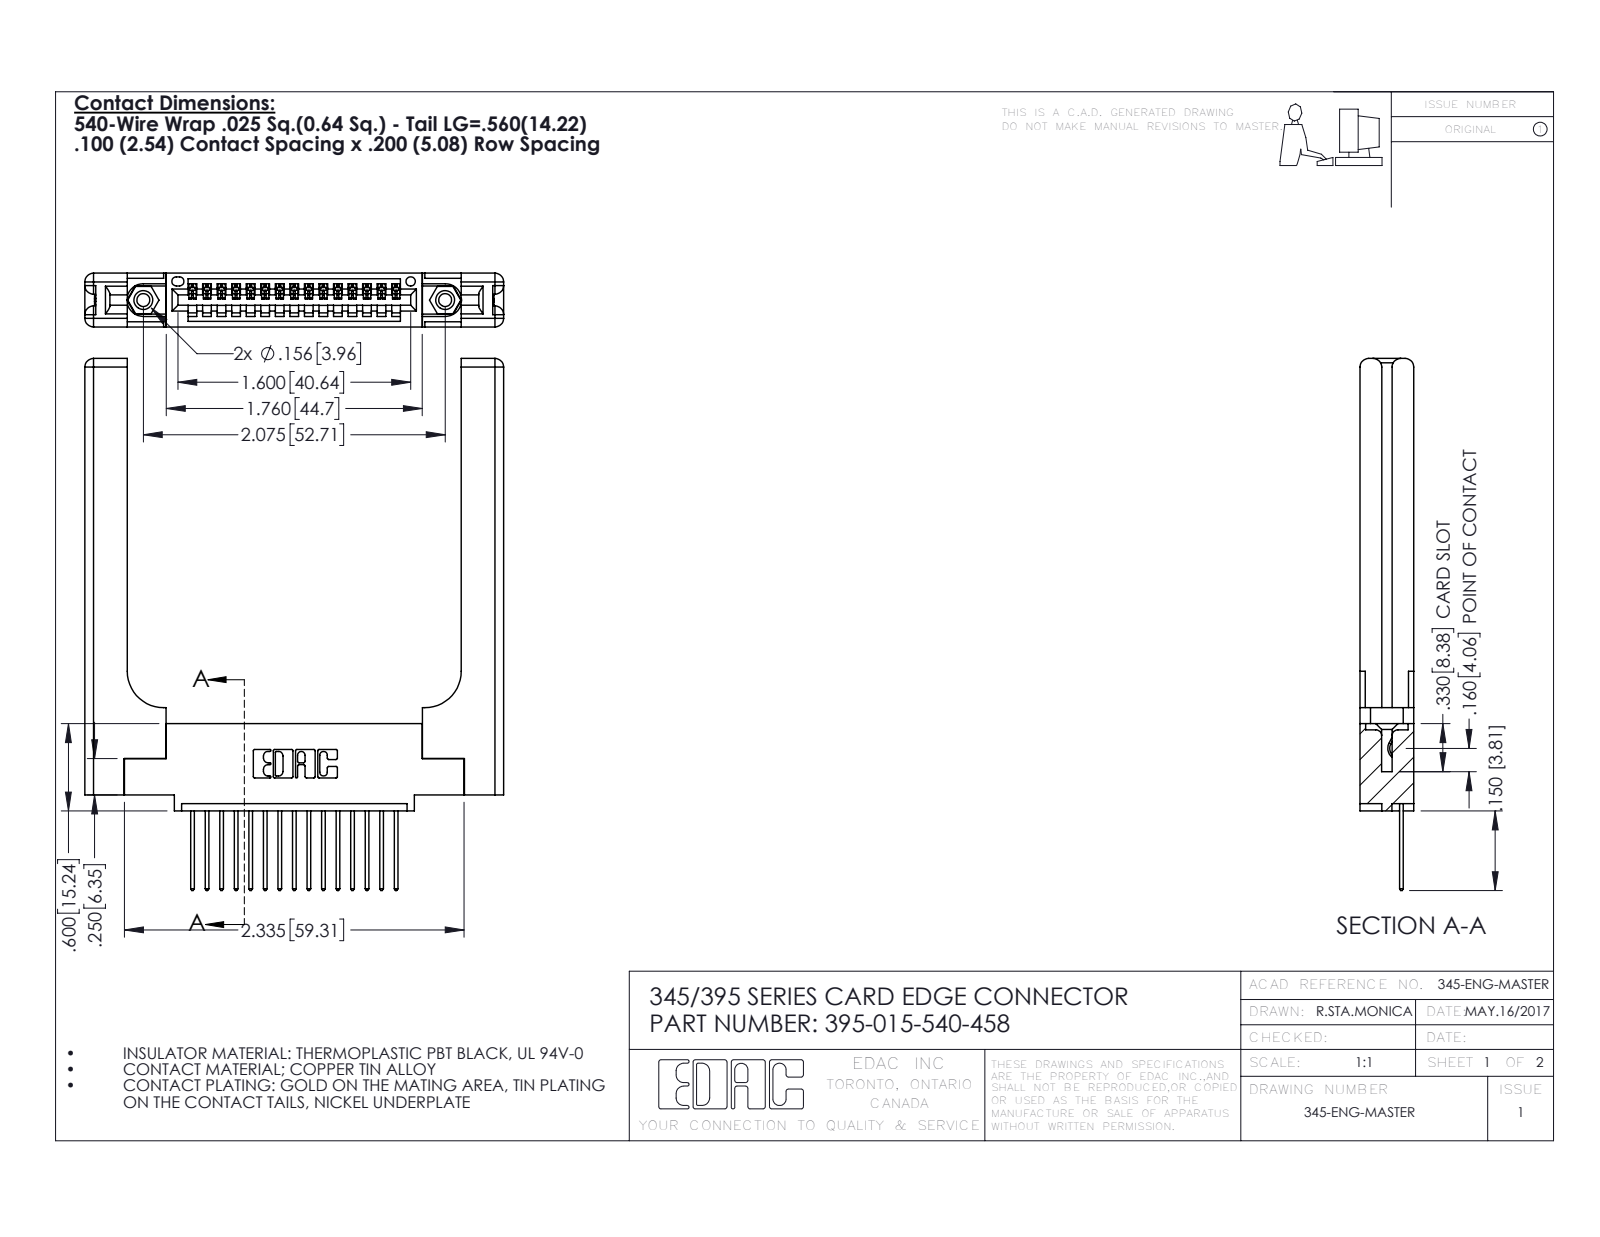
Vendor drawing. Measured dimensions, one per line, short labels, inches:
name: 345-220-058_345-220-058; 345 Part_0.110 Offset - 0.156 Dia-TH; 345-250-001_345-250-001-102; 395-015-540-458 (+1 more)
written by: SolidWorks 2016 (CONFIG_CONTROL_DESIGN)
unit: in
bodies: 20 solids, 1256 faces (832 planar, 364 cylindrical, 60 other)
size: 3.657 × 2.879 × 0.37
volume: 0.926 in³; area: 21.75 in²
holes: 2× ⌀0.089, 2× ⌀0.125, 2× ⌀0.156, 1× ⌀0.064
bosses: 2× ⌀0.155
rounds: 30× R0.006, 30× R0.01, 22× R0.01, 16× R0.06, 6× R0.007, 6× R0.031, 3× R0.026, 2× R0.03
face distances: 0.37, 0.072, 0.298, 0.15, 0.148, 0.077, 0.22, 0.098, 0.272, 0.025
hole spacings: 0.27, 1.842, 2.075
